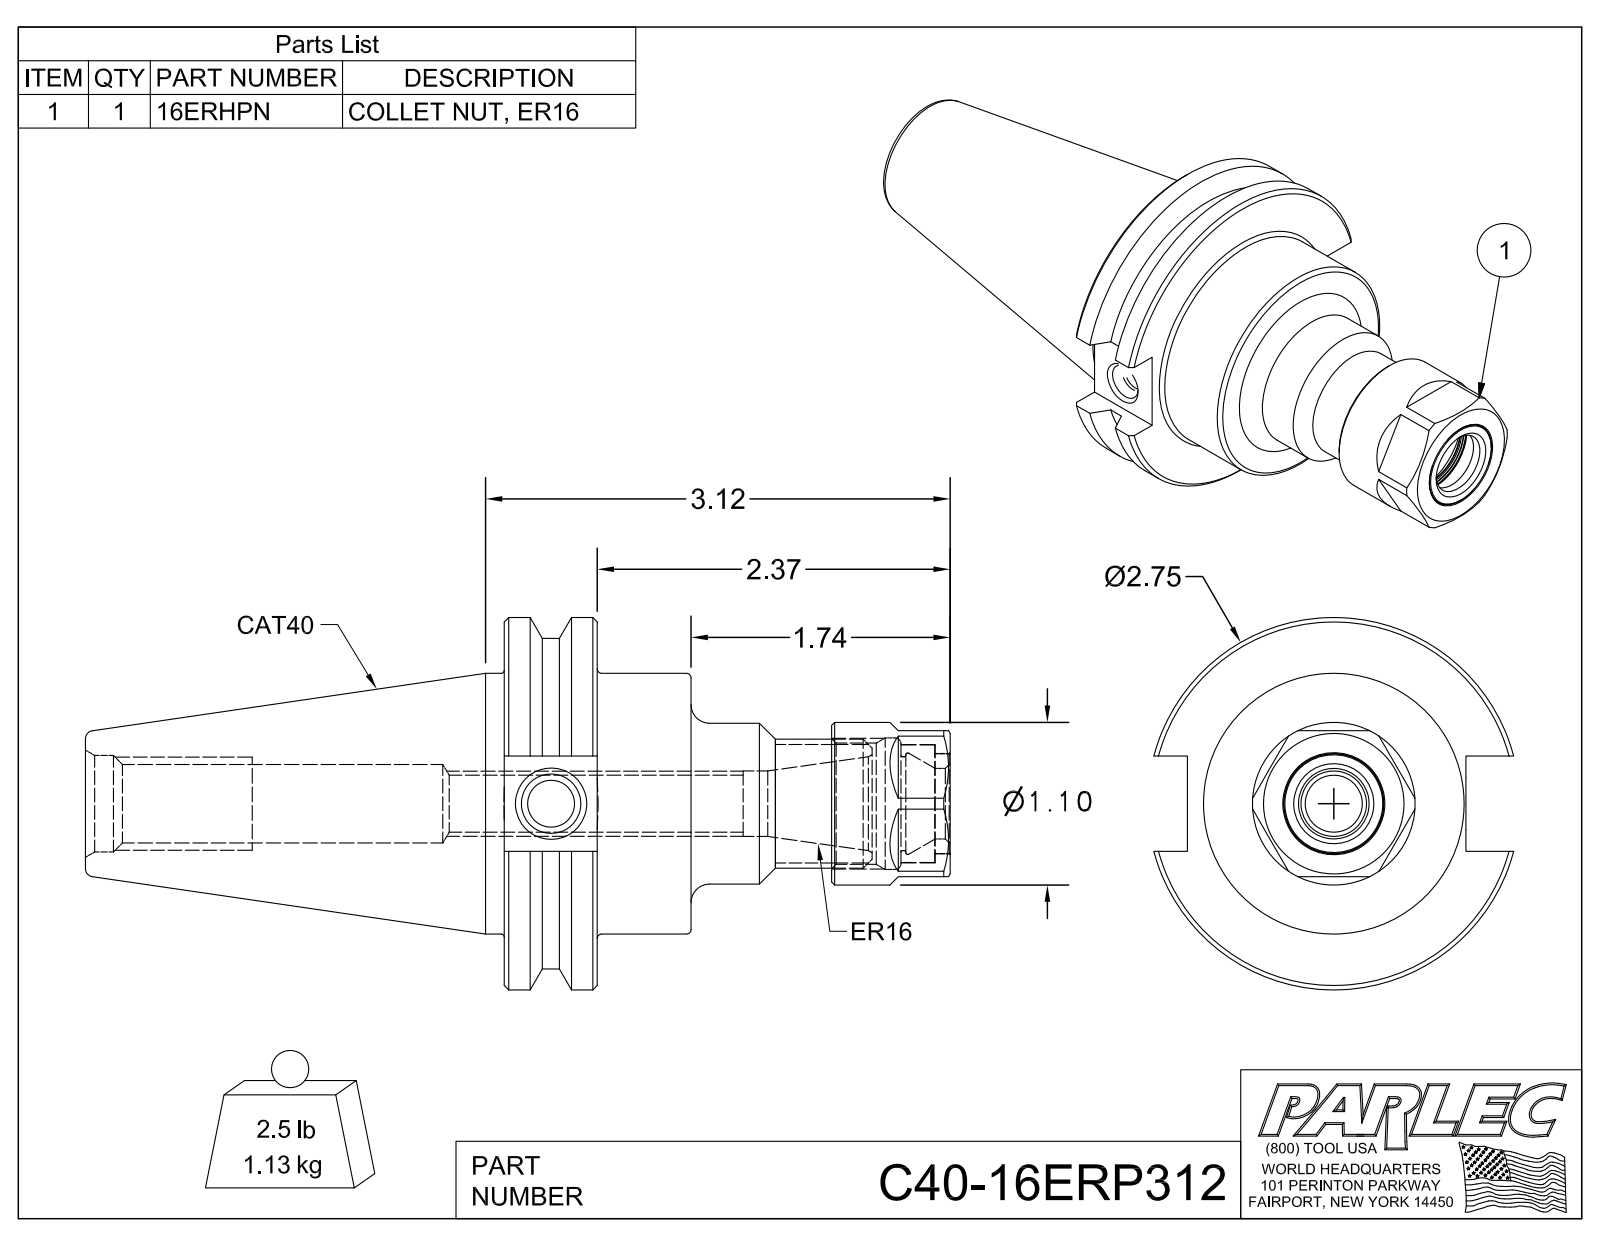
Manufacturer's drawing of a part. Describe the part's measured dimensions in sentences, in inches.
The part is named "C40-16ERP312; C40-16ER3-1; 16ERHPN". Its 3-D file was written by "Autodesk Inventor 2018 (AUTOMOTIVE_DESIGN)". It is 3 solids with 95 faces: 33 planar, 26 cylindrical and 36 other. Overall it measures 5.808 by 2.5 by 2.417 inches. Its volume is 8.712 cubic inches and its surface area 47.42 square inches. Round holes: 1 of diameter 0.315, 1 of diameter 0.383, 1 of diameter 0.399, 1 of diameter 0.44, 1 of diameter 0.474, 1 of diameter 0.527, 1 of diameter 0.63, 1 of diameter 0.648, 1 of diameter 0.674, 1 of diameter 0.68, 1 of diameter 0.794, 1 of diameter 0.814. Round bosses or shafts: 1 of diameter 2.5, 1 of diameter 2.219, 1 of diameter 1.75, 1 of diameter 1.092, 1 of diameter 1.08, 1 of diameter 0.866, 1 of diameter 0.79, 1 of diameter 0.67. The main face-to-face distances are 0.625, 1.255, 0.63, 0.98, 2.995, 2.37, 1.74, 0.17, 0.81, 0.64.
